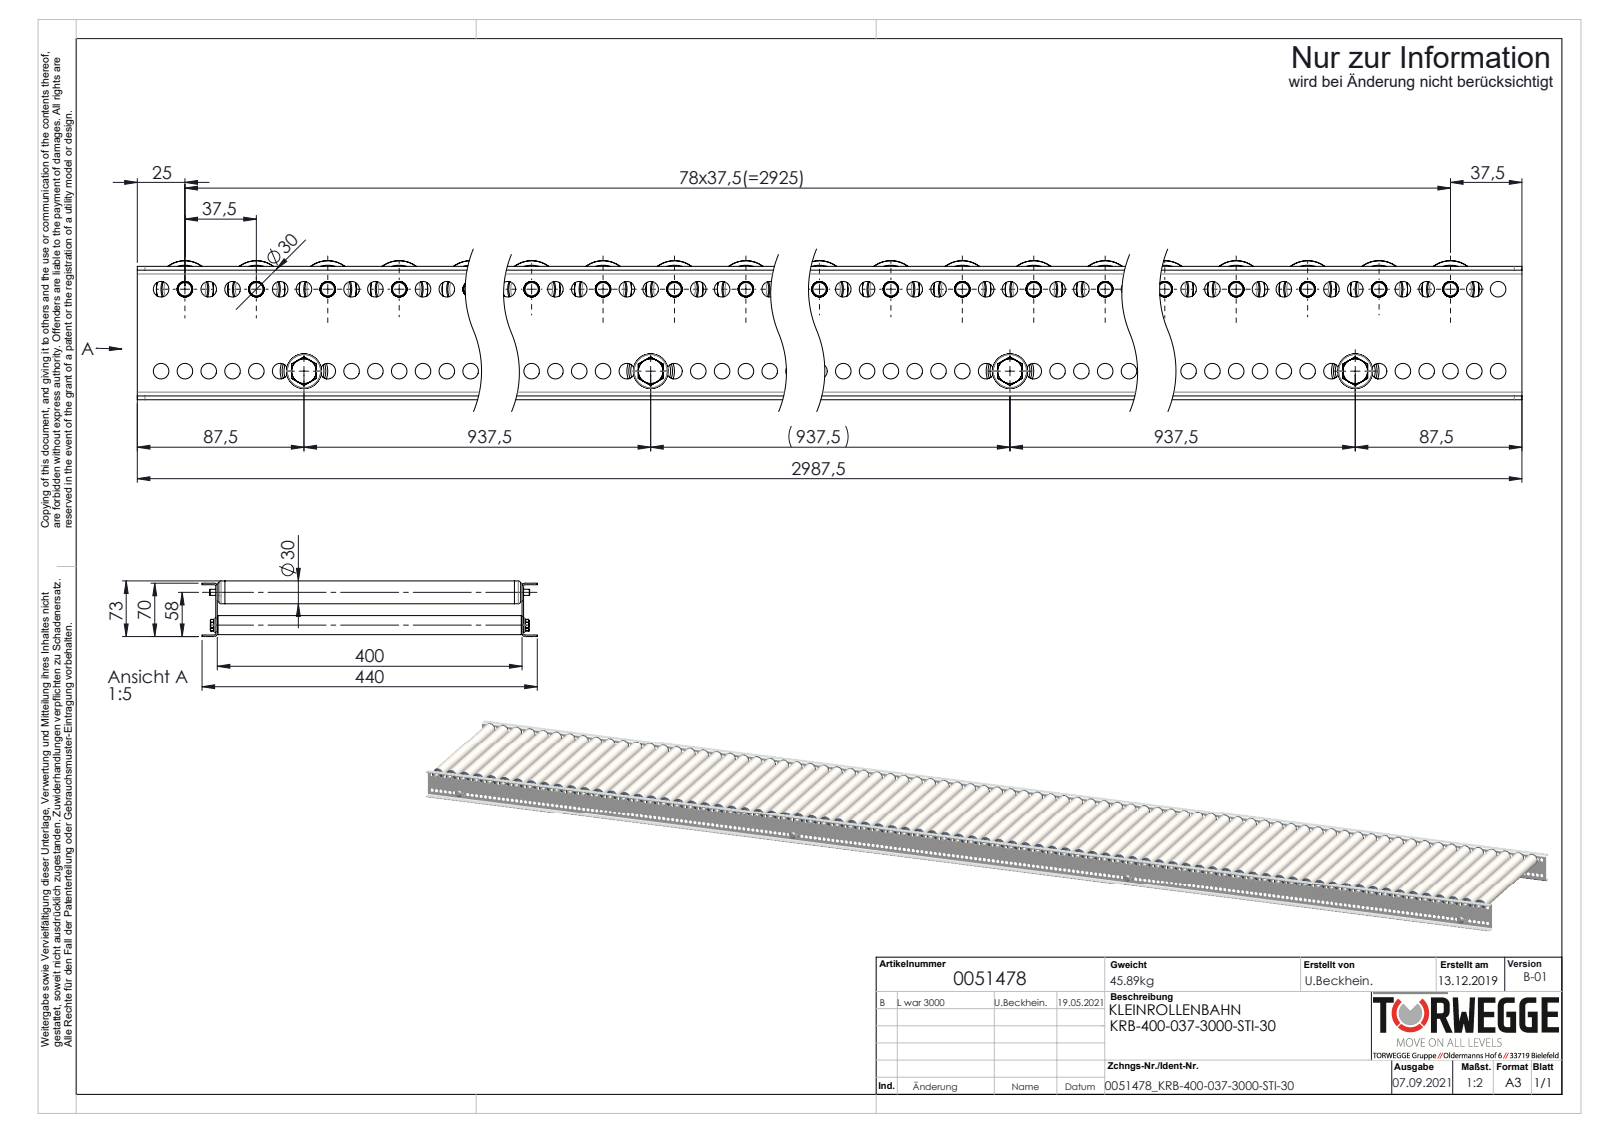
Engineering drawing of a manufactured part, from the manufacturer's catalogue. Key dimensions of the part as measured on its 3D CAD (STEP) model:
Part name (STEP PRODUCT): Profil_KRB-20x70x20x2_KFG_S109079_U-PROFIL-20-70-20-2-KRB-30-L=2987,5; 0042503_Typ-KUT50-30x1,5-A8; Traversen_KFG_L400; 0039768_Tragrollenrohr-Ø30x1,5STI_KFG_0039768_L=380 (+6 more)
STEP written by: SolidWorks 2020 (AUTOMOTIVE_DESIGN)
Units: millimetres
Bodies: 496 solids, 20898 faces (6524 planar, 8320 cylindrical, 6054 other)
Overall size (bounding box): 2987.5 × 440 × 73
Volume: 7 171 000 mm³ · Surface area: 8 816 000 mm²
Round holes (diameter × count): ⌀8.2 ×476, ⌀8 ×79, ⌀8.1 ×79, ⌀23.2 ×79, ⌀25.2 ×79, ⌀27 ×79, ⌀6.8 ×4, ⌀21 ×4
Round bosses / shafts (diameter × count): ⌀30 ×79, ⌀29.9 ×79, ⌀27.1 ×79, ⌀26.8 ×79, ⌀24 ×79, ⌀14 ×79, ⌀25 ×4, ⌀8 ×4
Partial cylindrical surfaces — rounded edges, fillets, slot ends (radius × count): R5.05 ×79, R4 ×8, R2 ×4
Main face-to-face distances: 2, 402, 400, 68, 404, 70, 66, 10, 390, 20
Hole centre spacings: 12.5, 25, 37.5, 50, 62.5, 75, 87.5, 100
